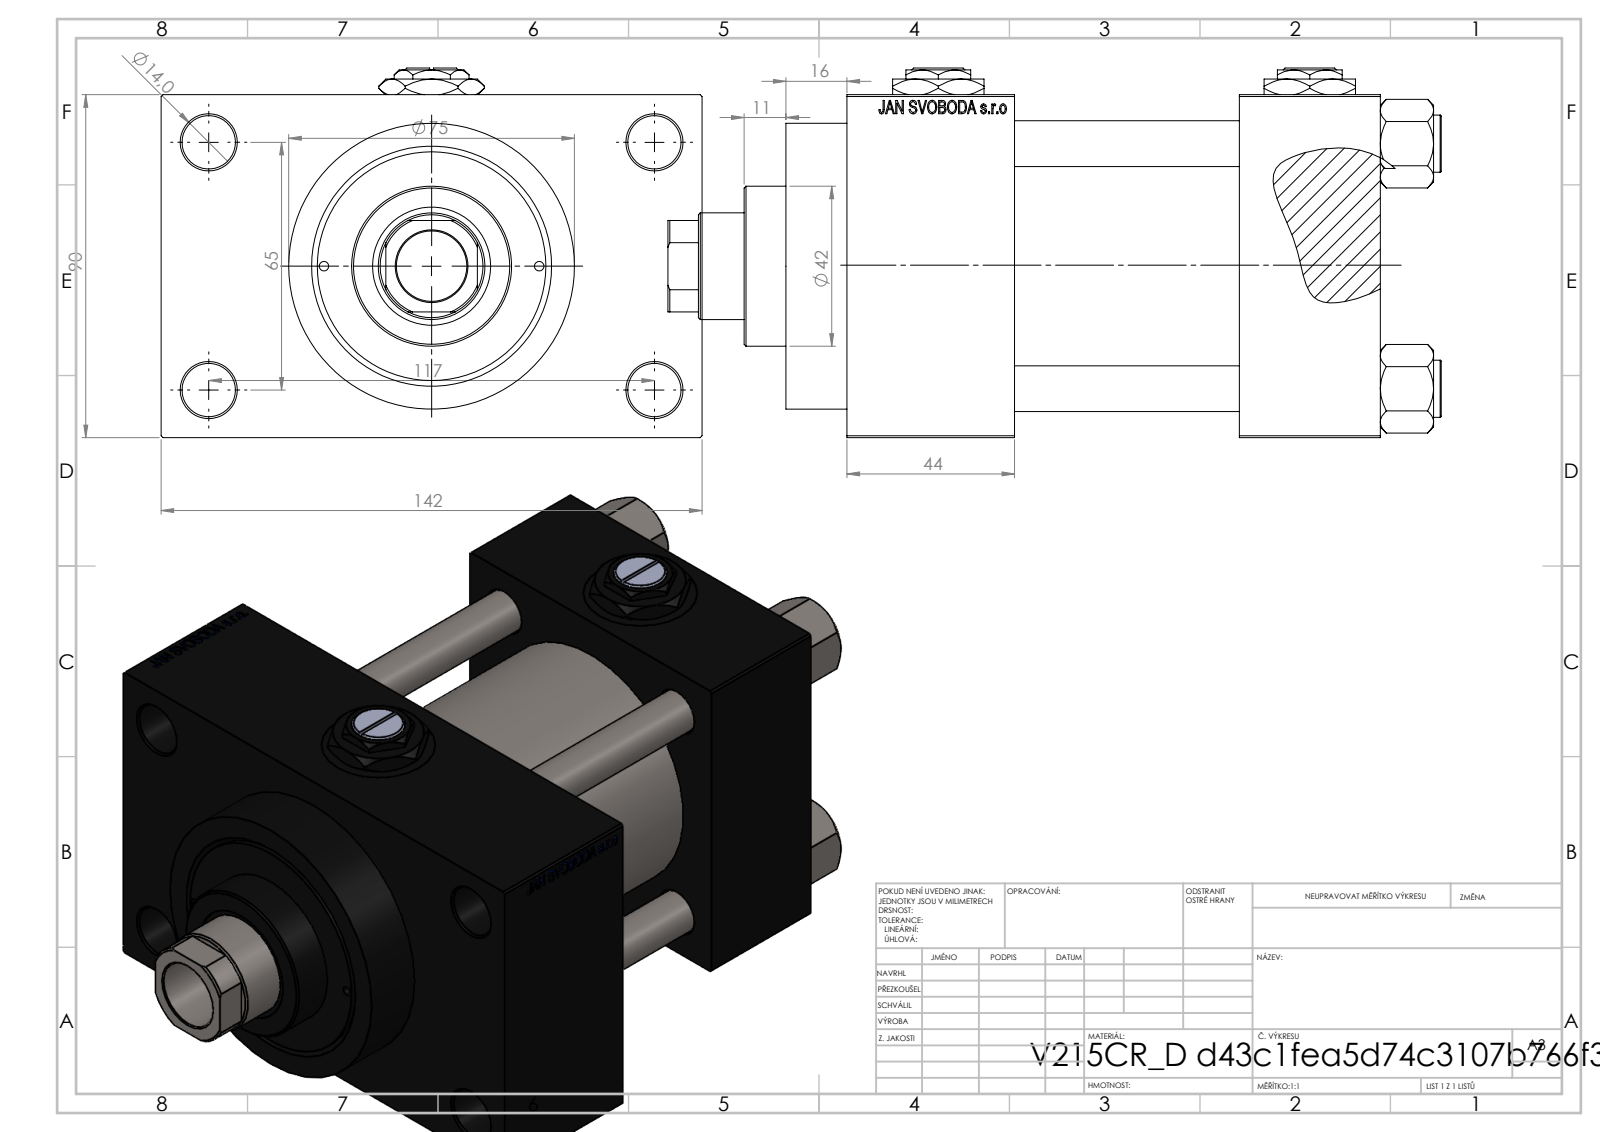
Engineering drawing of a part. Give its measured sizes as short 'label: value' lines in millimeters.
name: V215CR_VCP_D; V215CR_D_TYCINKA; NUT_M5_D; Zatka_pro_OIL_PORT (+2 more)
written by: SolidWorks 2019 (CONFIG_CONTROL_DESIGN)
unit: mm
bodies: 13 solids, 1212 faces (547 planar, 103 cylindrical, 562 other)
size: 203 × 142 × 97
volume: 1 090 000 mm³; area: 204 858 mm²
holes: 4× ⌀12, 4× ⌀14, 4× ⌀20.96, 4× ⌀30, 3× ⌀7, 2× ⌀2.5, 1× ⌀18.5, 1× ⌀28, 1× ⌀31, 1× ⌀50, 1× ⌀60, 1× ⌀63
bosses: 4× ⌀15, 1× ⌀75, 1× ⌀69, 1× ⌀42
rounds: 1× R13.5
face distances: 90, 59, 37, 96, 140, 103, 44, 26, 116, 142
hole spacings: 26.35, 32.39, 44.4, 45.47, 64.3, 66.92, 68.42, 69.81
